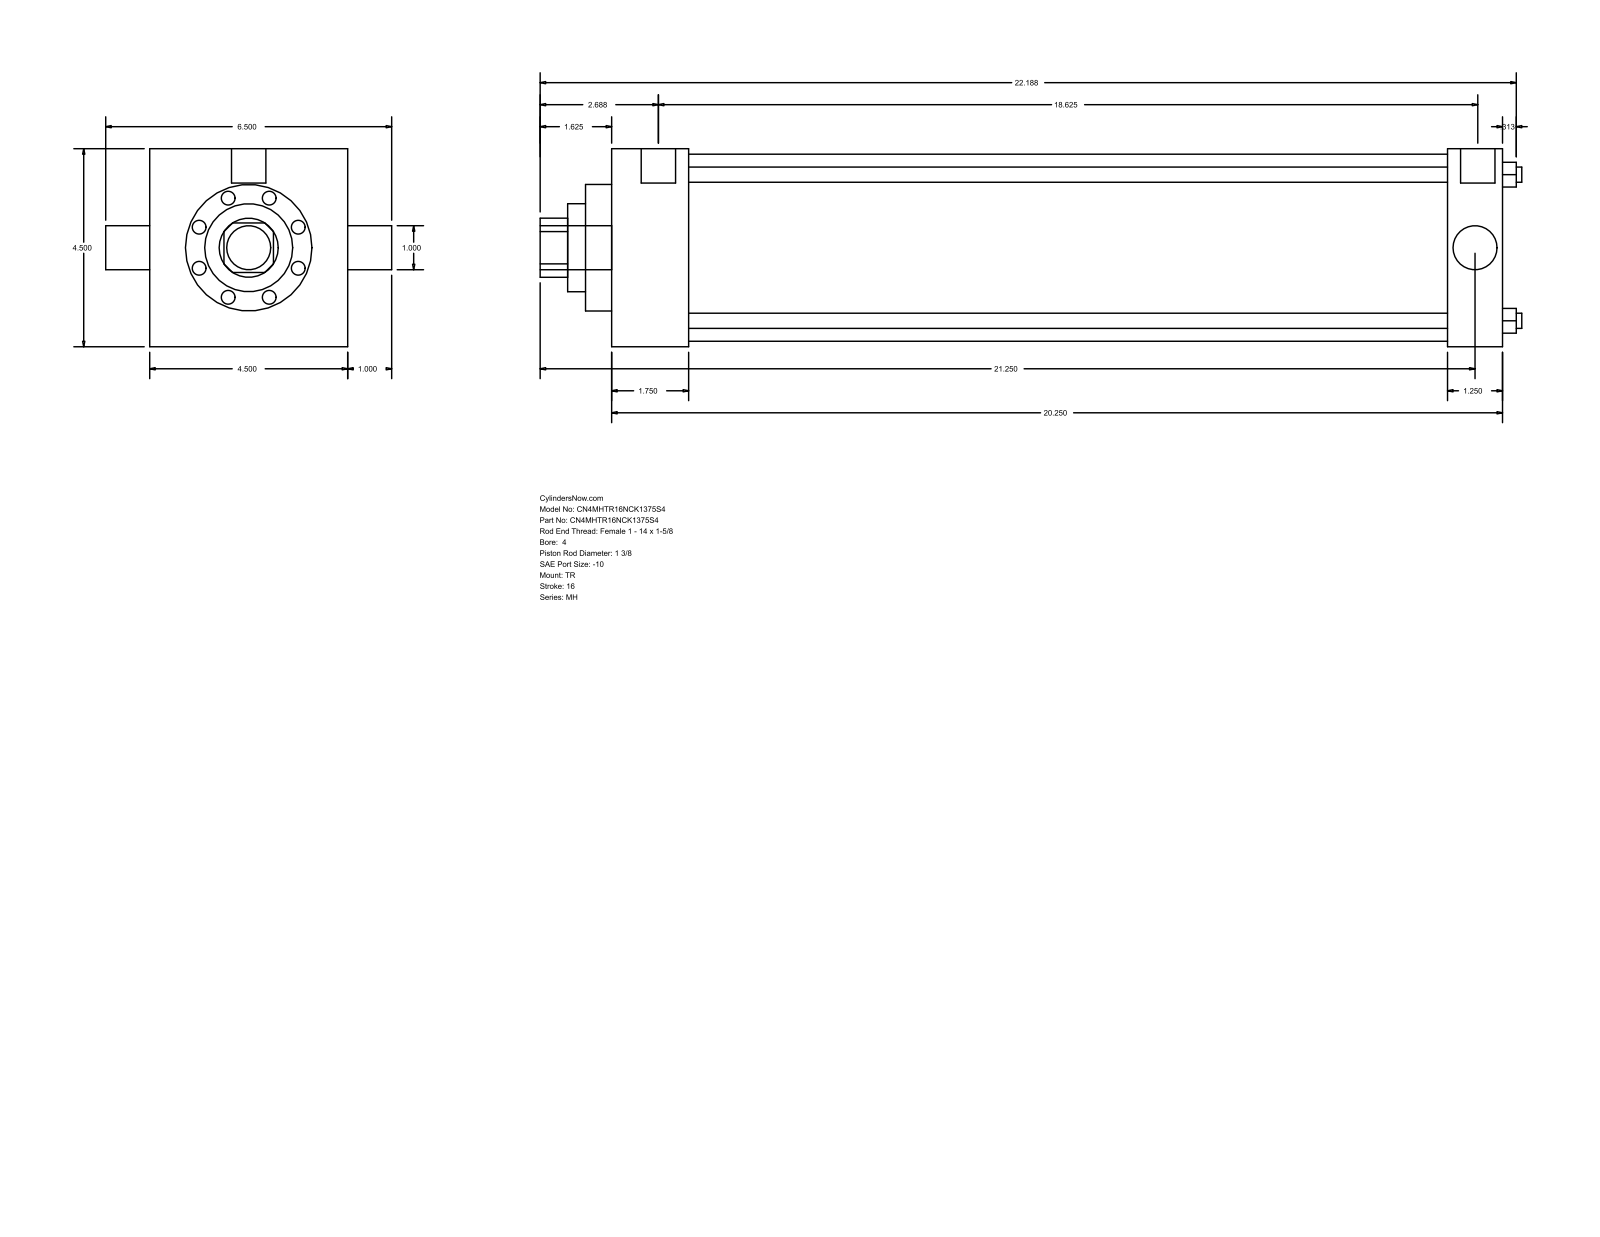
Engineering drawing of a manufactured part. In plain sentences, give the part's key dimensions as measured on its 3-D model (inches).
The part is named "MH_TR__0400_1.375". Its 3-D file was written by "GSSL Pune (CONFIG_CONTROL_DESIGN)". It is 0 solids with 86 faces: 61 planar, 25 cylindrical and 0 other. Overall it measures 22.313 by 6.5 by 4.5 inches. Round holes: 4 of diameter 0.345, 1 of diameter 1, 1 of diameter 1.375, 1 of diameter 2, 1 of diameter 2.875, 1 of diameter 4.25. Round bosses or shafts: 3 of diameter 0.344, 2 of diameter 0.781, 1 of diameter 1. Partial cylindrical surfaces (rounded edges, fillets, slot ends): 1 of radius 0.672. The main face-to-face distances are 4.5, 20.25, 1.75, 18.5, 19, 17.25, 1.25, 0.594, 2.344, 19.594. The hole center spacings are 2.347, 3.32, 4.695.
